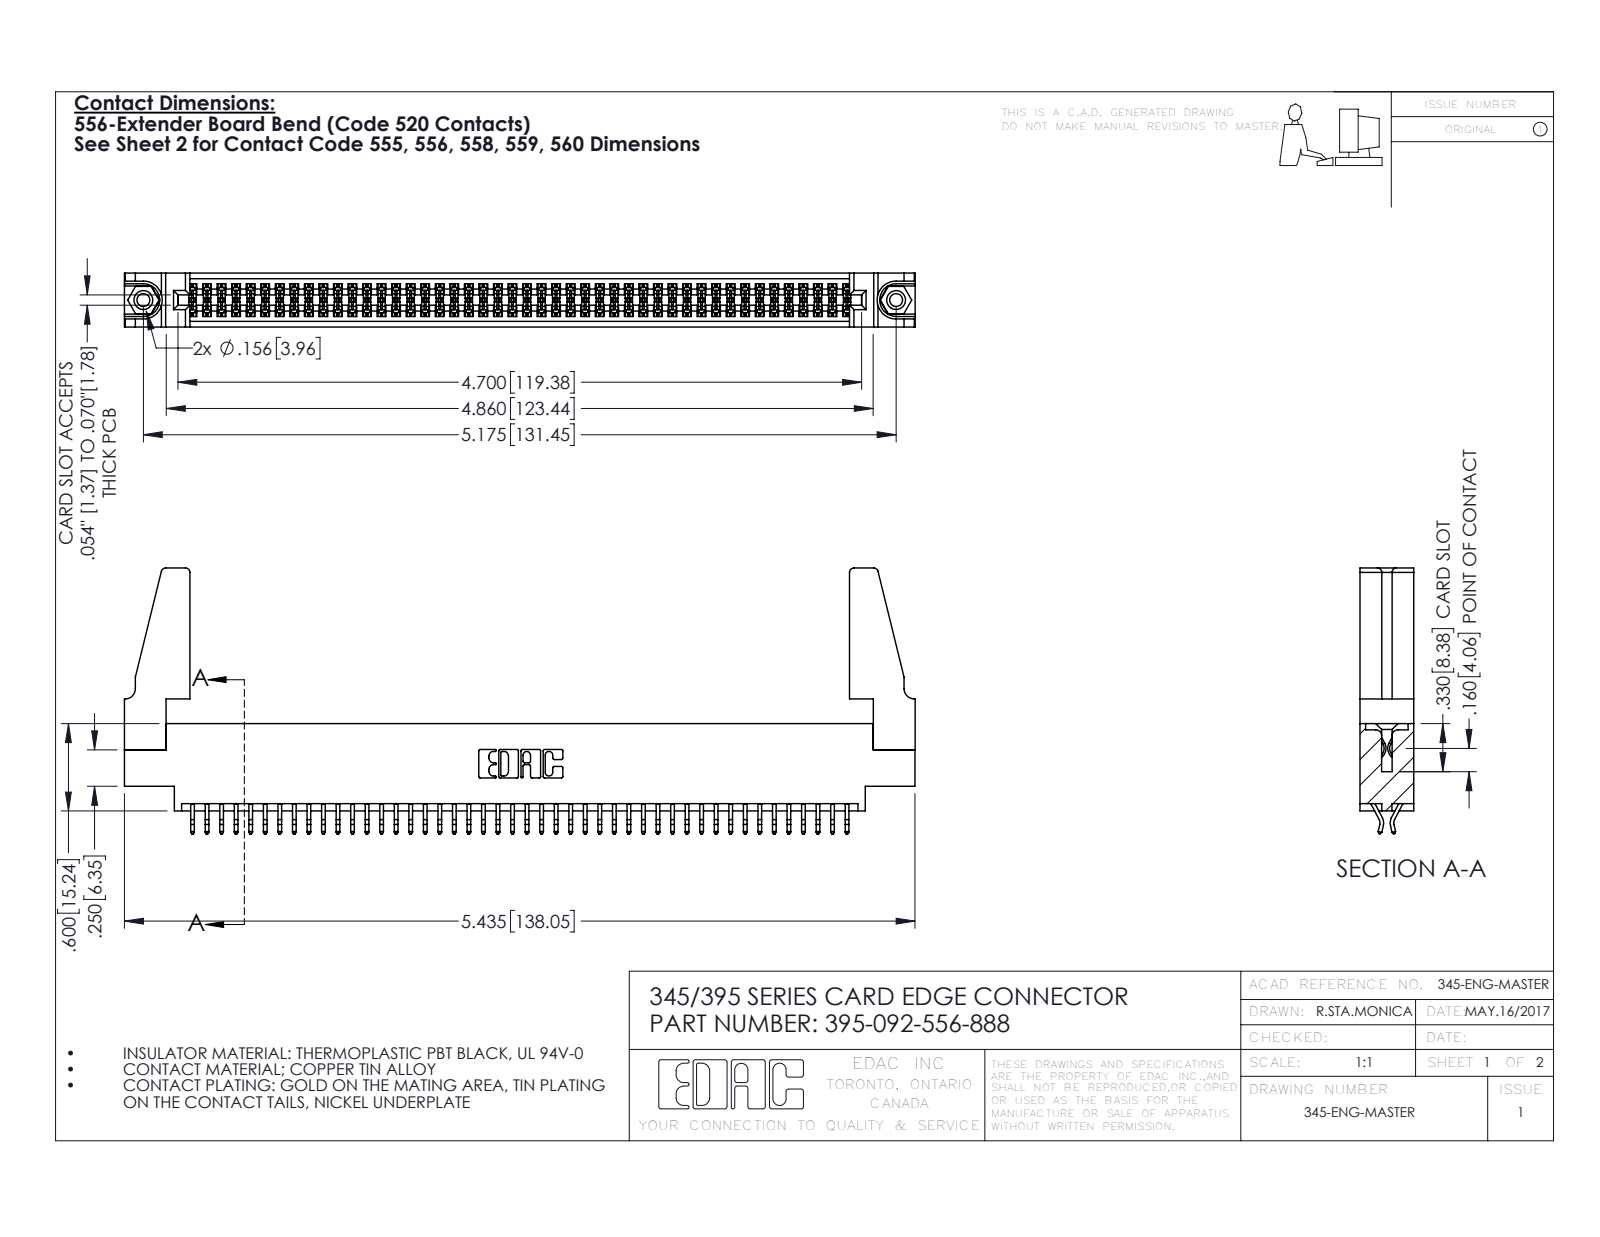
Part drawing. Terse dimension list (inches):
name: 345-220-078_345-220-088; 345-292-001_556 Tail; 395-092-556-888; 345 Part_0.170 Offset - 0.156 Dia-TH (+1 more)
written by: SolidWorks 2016 (CONFIG_CONTROL_DESIGN)
unit: in
bodies: 97 solids, 5406 faces (3560 planar, 1830 cylindrical, 16 other)
size: 5.436 × 1.827 × 0.37
volume: 1.012 in³; area: 35.6 in²
holes: 2× ⌀0.089, 2× ⌀0.125, 2× ⌀0.156, 1× ⌀0.064
bosses: 2× ⌀0.155
rounds: 138× R0.006, 22× R0.01, 8× R0.03, 6× R0.007, 6× R0.031, 3× R0.026, 2× R0.01, 2× R0.014
face distances: 0.072, 0.298, 0.37, 0.025, 0.2, 0.098, 0.272, 0.225, 0.175, 0.149
hole spacings: 0.27, 4.939, 5.175
